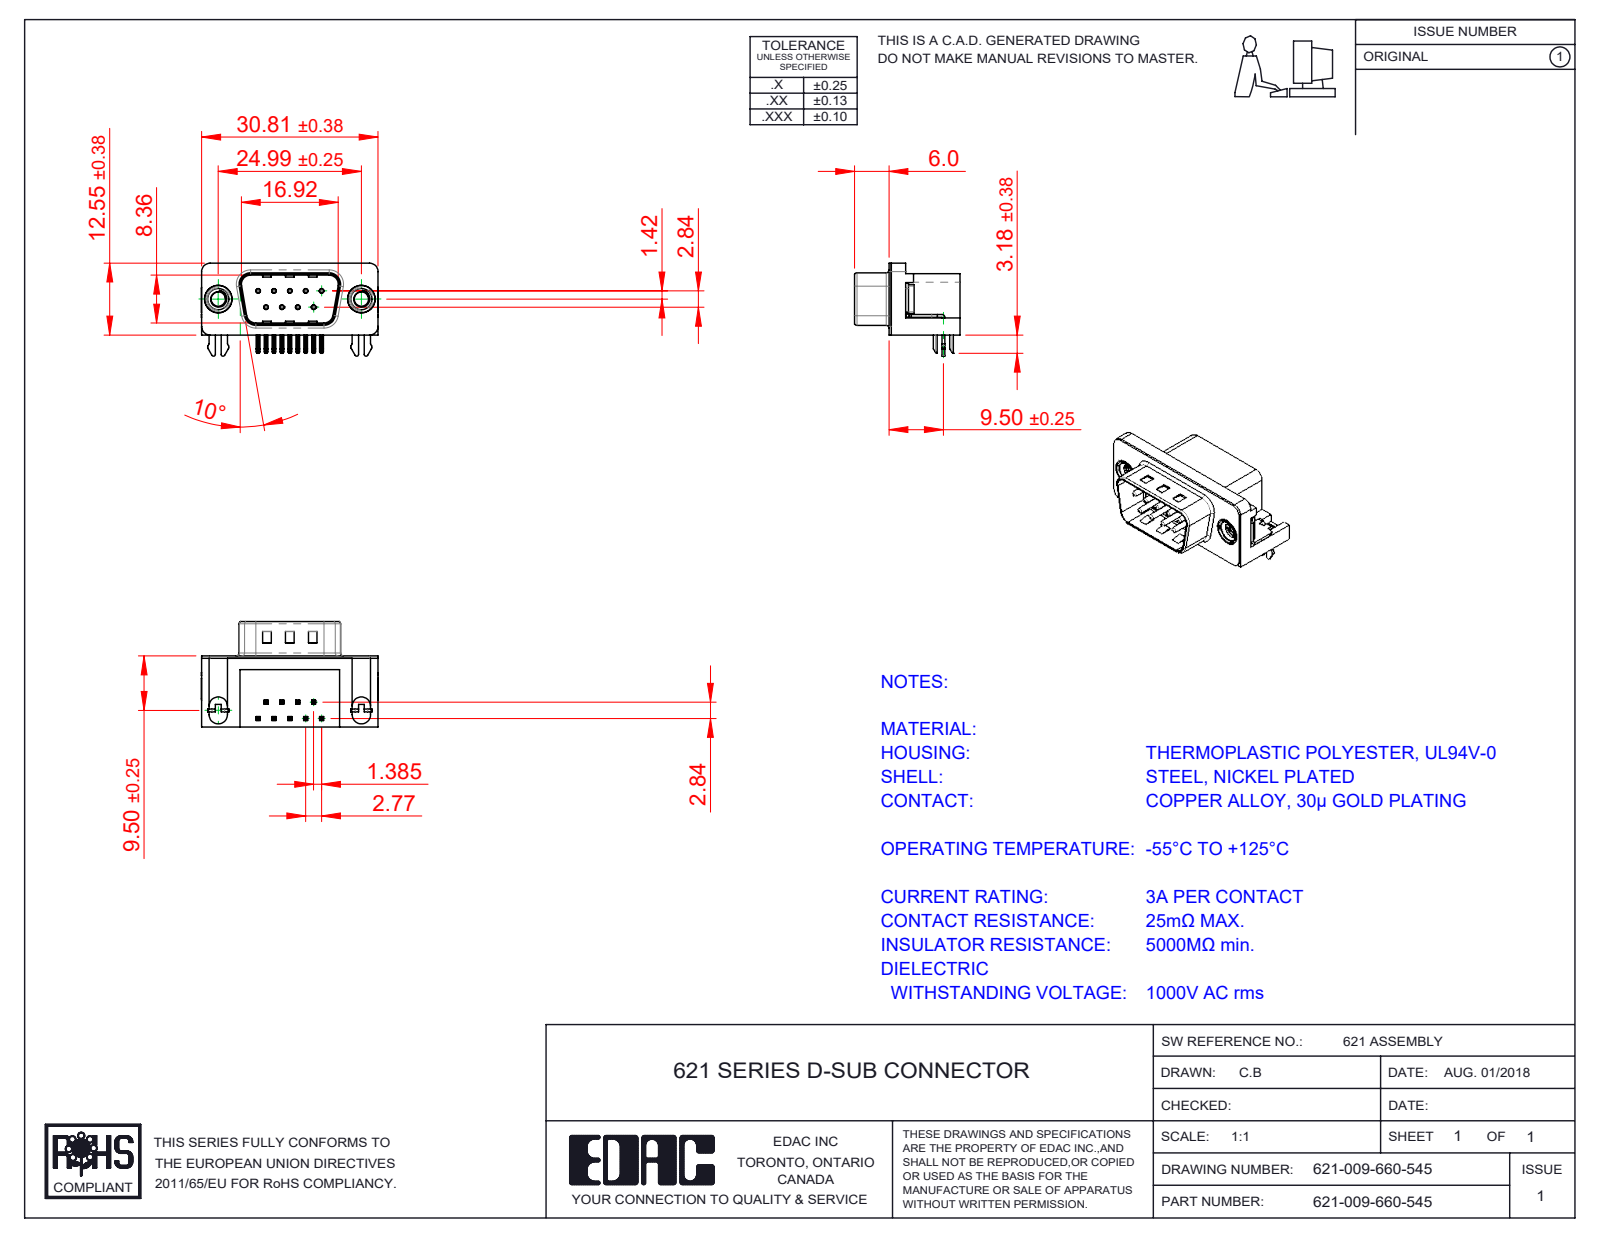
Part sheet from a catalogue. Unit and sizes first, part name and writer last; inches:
Units: inches
Overall size (bounding box): 1.216 × 0.724 × 0.64
Round holes (diameter × count): ⌀0.014 ×9, ⌀0.031 ×9, ⌀0.079 ×2, ⌀0.098 ×2, ⌀0.157 ×2, ⌀0.189 ×2, ⌀0.197 ×2
Round bosses / shafts (diameter × count): ⌀0.03 ×9, ⌀0.193 ×2, ⌀0.187 ×2, ⌀0.154 ×2, ⌀0.118 ×2
Partial cylindrical surfaces — rounded edges, fillets, slot ends (radius × count): R0.01 ×48, R0.005 ×18, R0.039 ×16, R0.02 ×9, R0.059 ×8, R0.063 ×8, R0.035 ×4, R0.079 ×4
Main face-to-face distances: 0.016, 0.472, 0.488, 0.407, 0.114, 0.374, 0.098, 0.083, 0.014, 0.421
Hole centre spacings: 0.124, 0.109, 0.218, 0.198, 0.198, 0.327, 0.294, 0.295
Volume: 0.198 in³ · Surface area: 6.973 in²
Bodies: 15 solids, 1111 faces (615 planar, 325 cylindrical, 171 other)
Part name (STEP PRODUCT): 621-009-660-545; 621 4 Prong Board Lock; 621 M3 Threaded Rivet; 621 Contact Top (+3 more)
STEP written by: SolidWorks 2016 (CONFIG_CONTROL_DESIGN)
